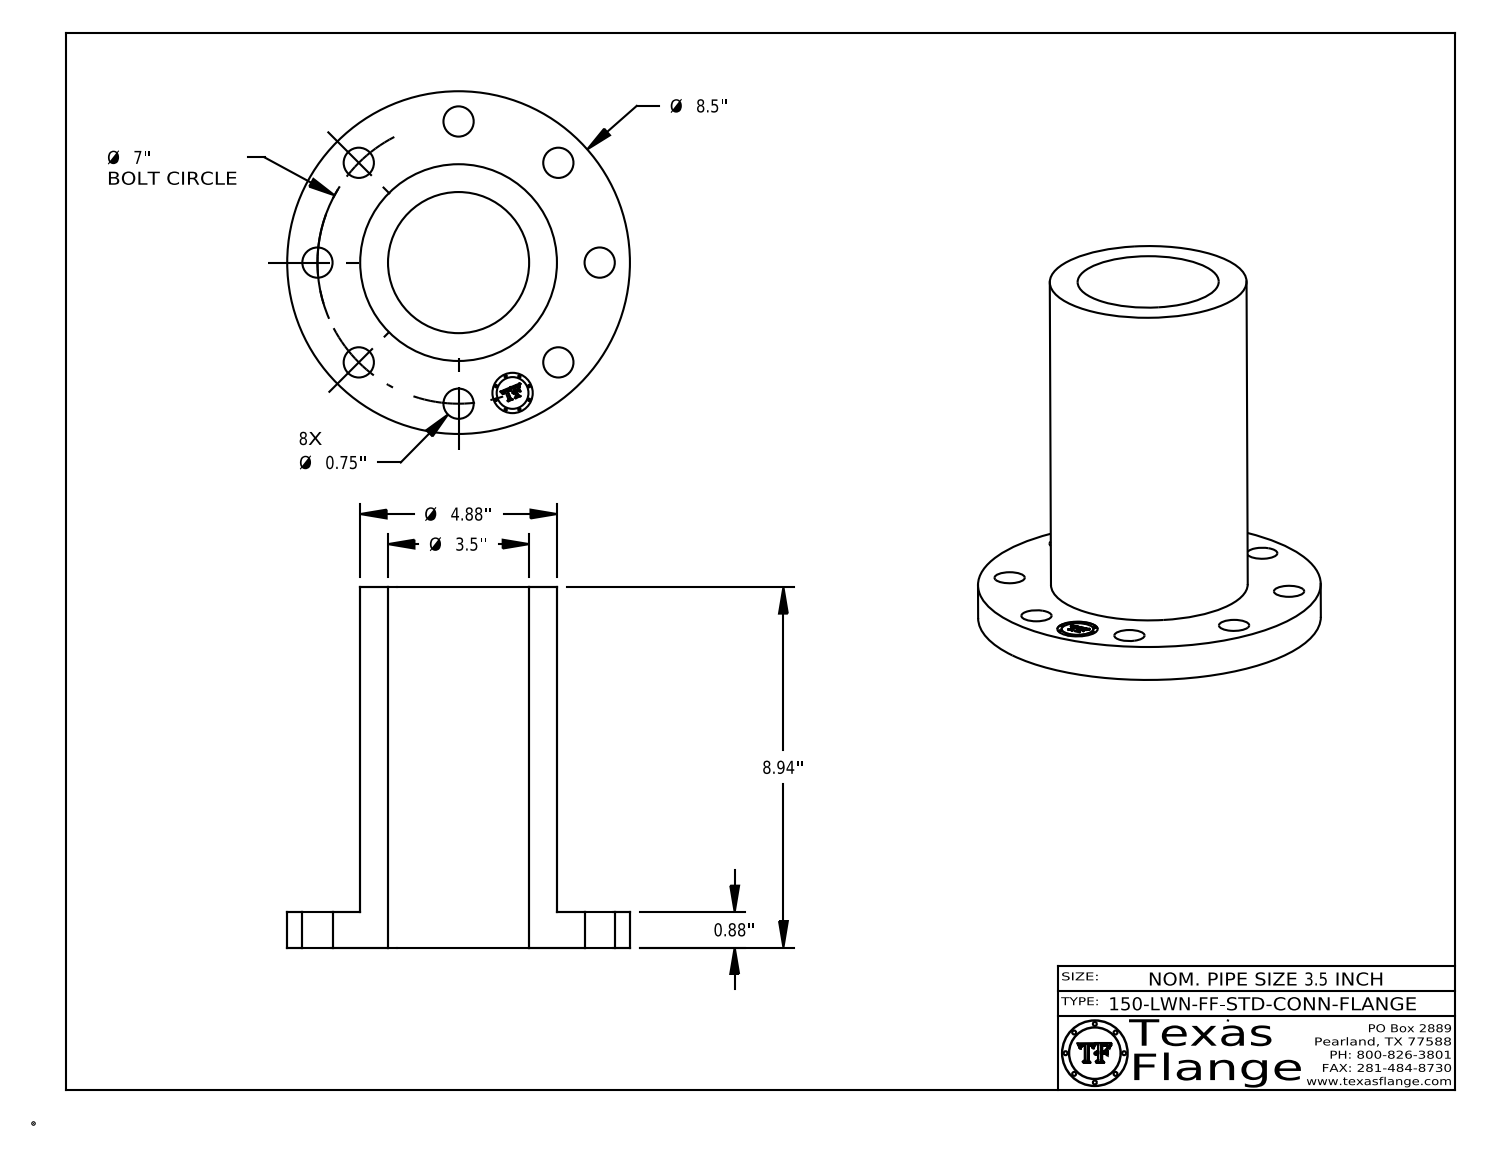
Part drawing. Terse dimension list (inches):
name: 3.5-150-LWN-FF-STD-CONN-FLANGE
written by: CATIA V5 STEP AP214 (AUTOMOTIVE_DESIGN)
unit: in
bodies: 1 solid, 410 faces (368 planar, 42 cylindrical, 0 other)
size: 8.938 × 8.5 × 8.5
volume: 111.5 in³; area: 349.1 in²
holes: 8× ⌀0.75, 1× ⌀1, 1× ⌀3.5
bosses: 8× ⌀0.061, 1× ⌀8.5, 1× ⌀4.88, 1× ⌀0.788
face distances: 0.878, 8.937, 8.06, 0.872, 8.065, 0.298, 0.293, 0.054, 0.193, 0.248
hole spacings: 3.5, 2.679, 4.95, 6.467, 1.366, 3.889, 5.82, 6.865
